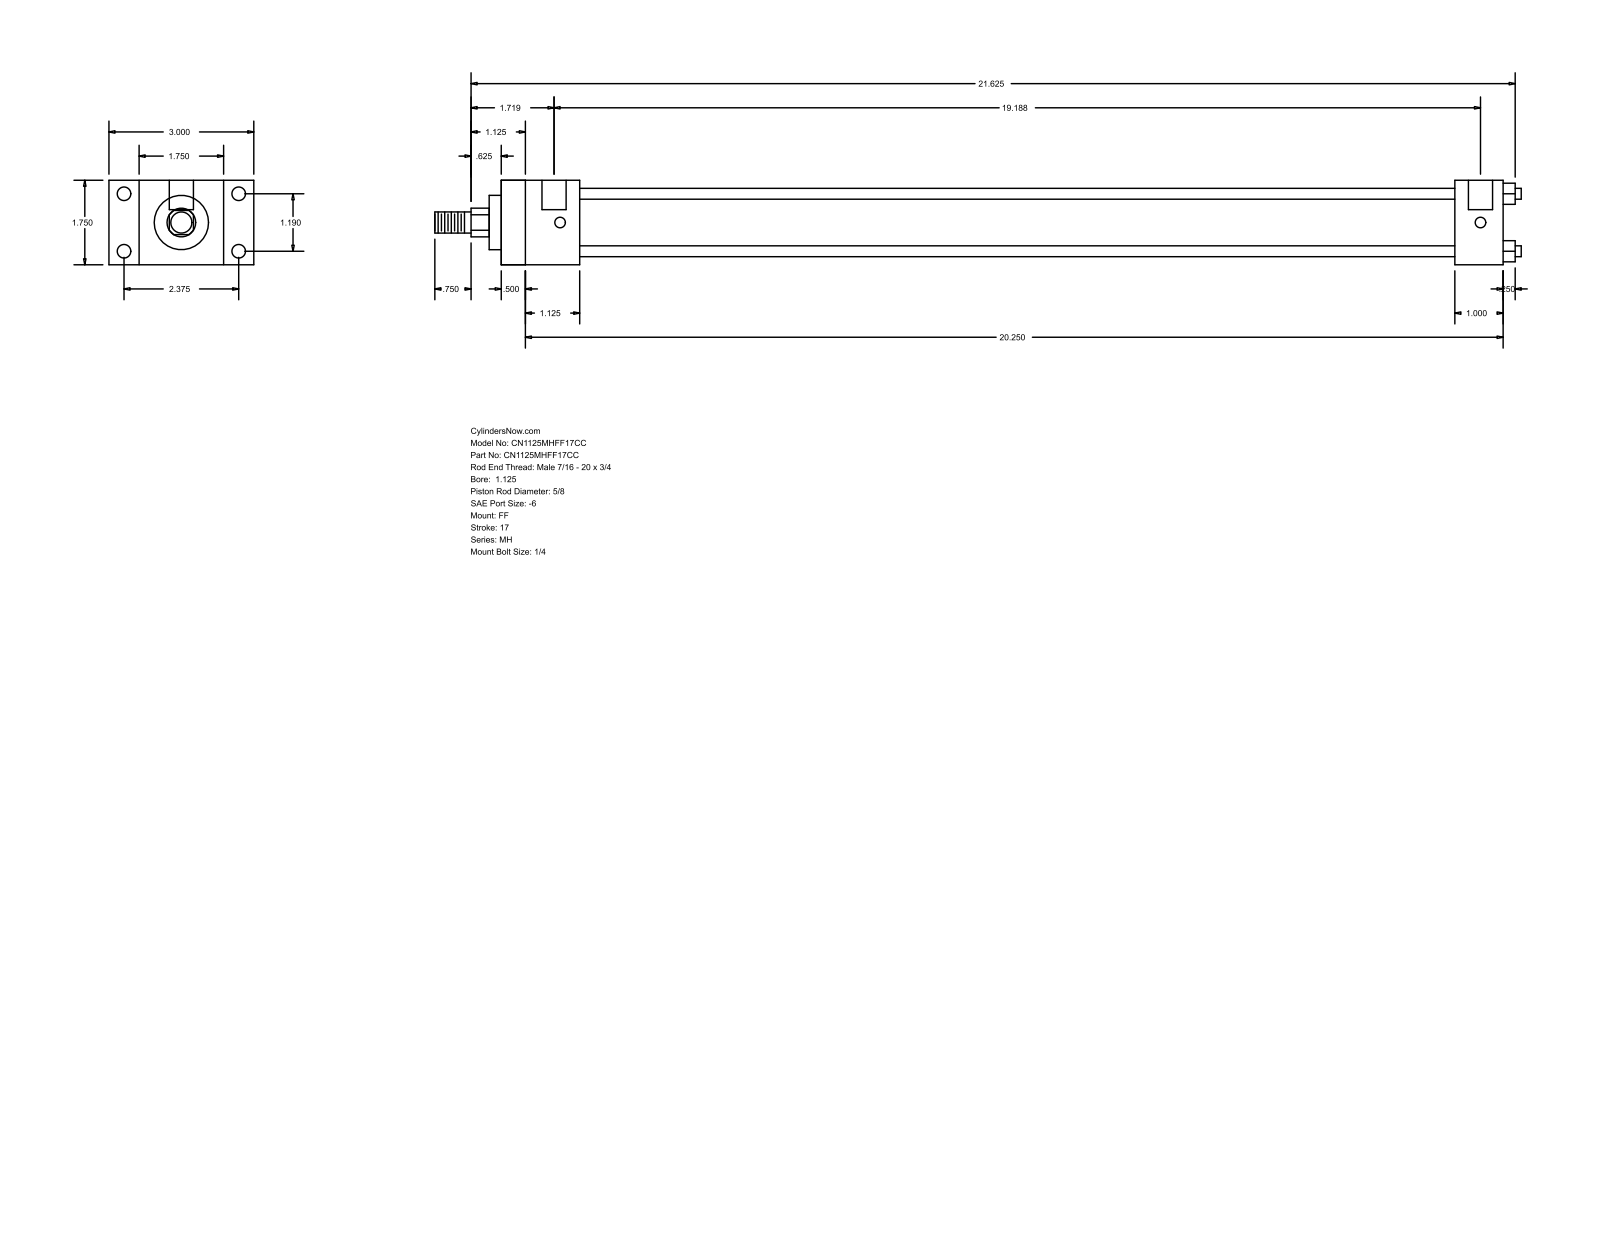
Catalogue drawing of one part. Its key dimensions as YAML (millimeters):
part_name: "MH_FF__0112_0.625"
step_written_by: "GSSL Pune (CONFIG_CONTROL_DESIGN)"
units: millimeters
bodies: {solids: 0, faces: 92, planar: 64, cylindrical: 28, other: 0}
overall_size: [571.5, 76.2, 44.45]
round_holes:
  - {diameter: 5.56, count: 4}
  - {diameter: 7.14, count: 4}
  - {diameter: 12.7, count: 2}
round_bosses_or_shafts:
  - {diameter: 5.71, count: 4}
  - {diameter: 34.92, count: 1}
  - {diameter: 28.57, count: 1}
  - {diameter: 15.88, count: 1}
  - {diameter: 11.11, count: 1}
partial_cylinders:
  - {radius: 7.54, count: 1}
face_to_face_distances: [44.46, 527.04, 12.69, 514.35, 15.87, 28.58, 60.33, 25.4, 41.27, 501.64]
hole_center_spacings: [30.22, 60.32, 67.47, 484.19, 3.17, 487.36]
